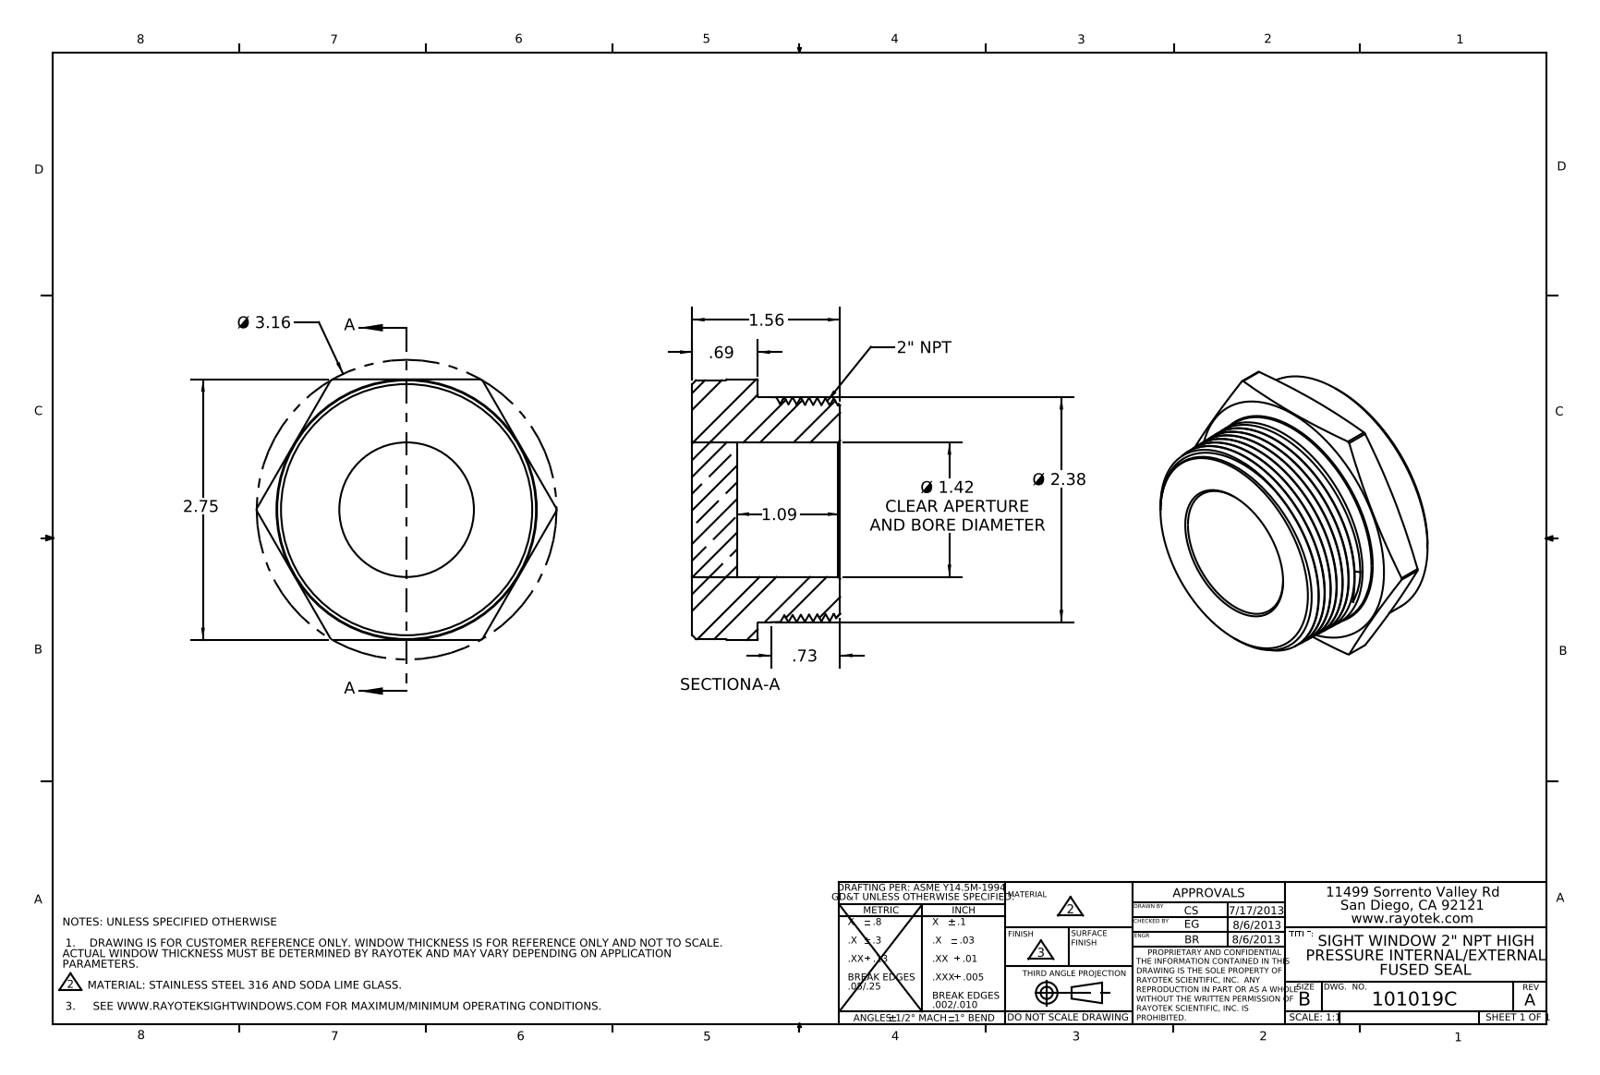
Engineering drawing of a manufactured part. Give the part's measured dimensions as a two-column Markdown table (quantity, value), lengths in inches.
| quantity | value |
| --- | --- |
| part name | 101019; 402019; 403019_CUSTOMER |
| STEP written by | SolidWorks 2012 (AUTOMOTIVE_DESIGN) |
| units | inches |
| bodies | 2 solids, 62 faces (14 planar, 15 cylindrical, 33 other) |
| overall size | 3.163 × 2.75 × 1.56 |
| volume | 6.154 in³ |
| surface area | 37.58 in² |
| round holes (diameter × count) | 1.42 × 1 |
| round bosses / shafts (diameter × count) | 2.73 × 1, 2.375 × 1 |
| partial cylindrical surfaces (radius × count) | 1.582 × 1 |
| main face-to-face distances | 1.56, 0.47, 1.09, 2.75, 0.69, 0.22, 0.87 |
